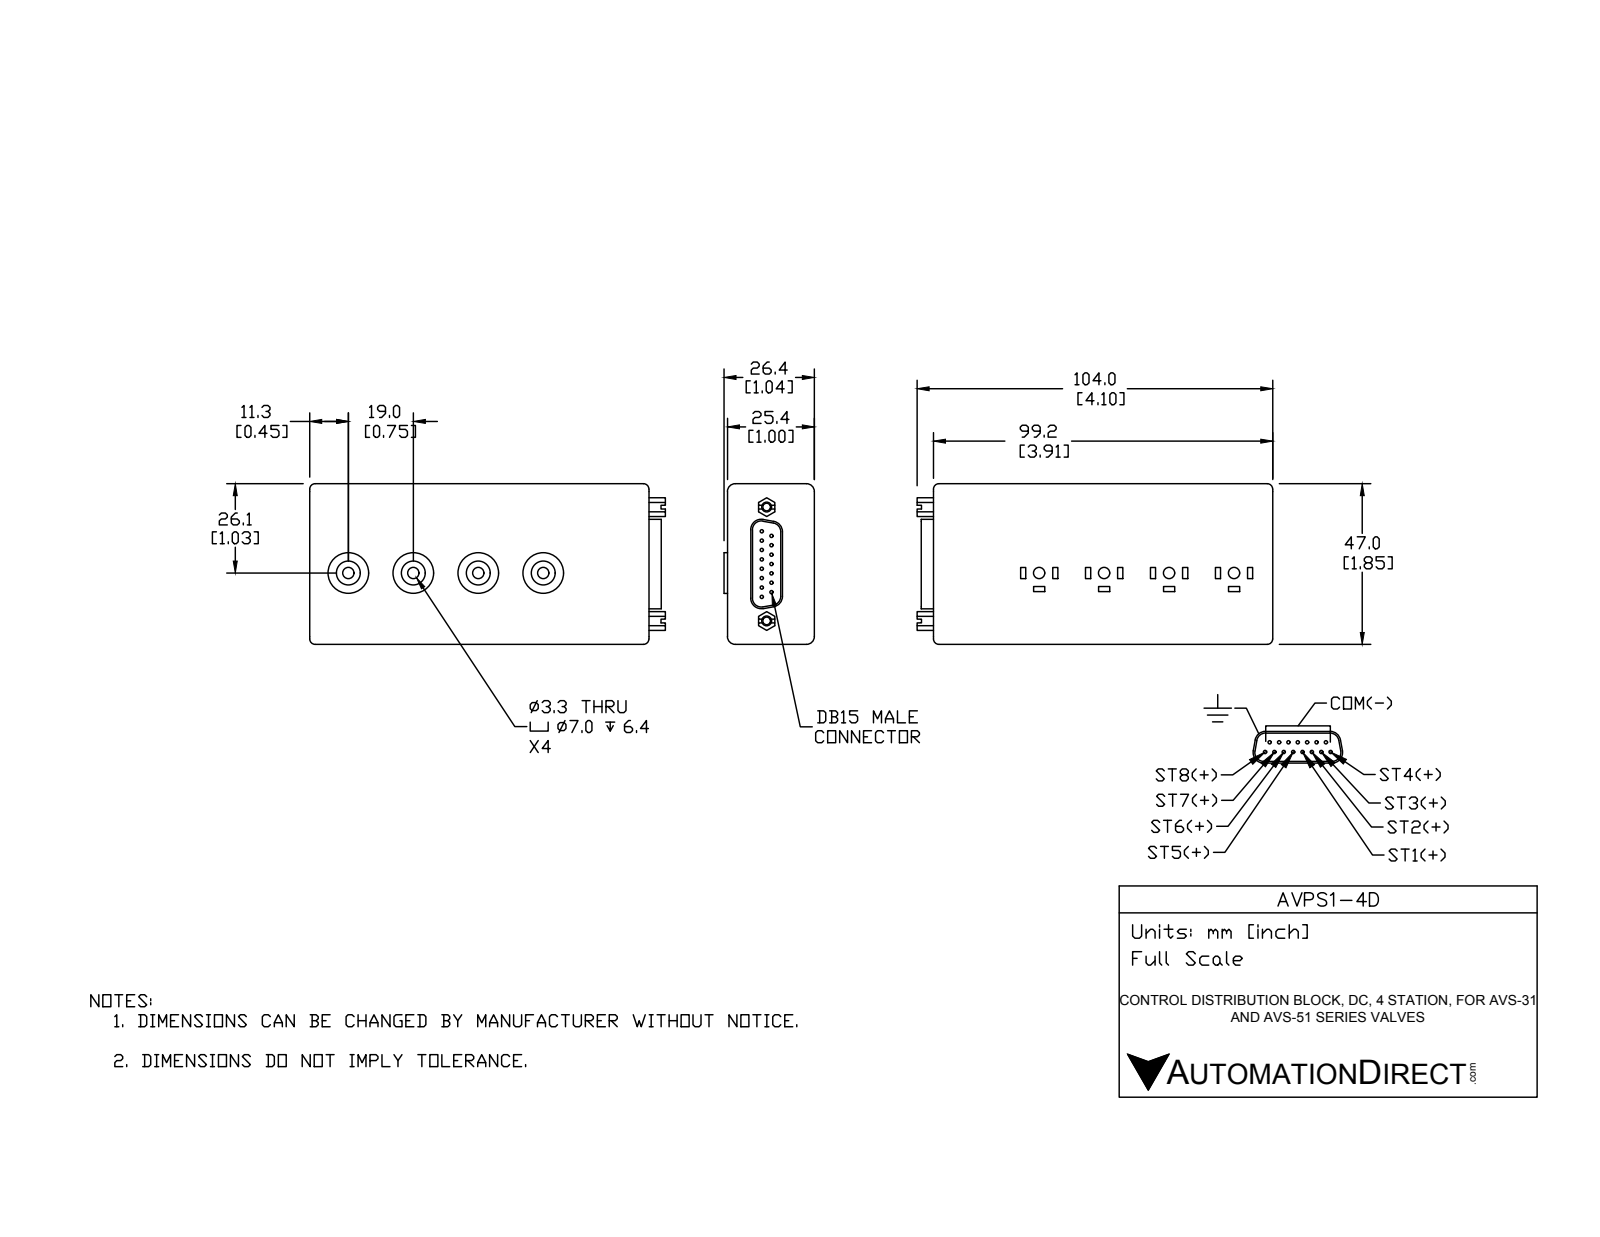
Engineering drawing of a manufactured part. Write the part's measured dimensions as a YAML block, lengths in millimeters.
part_name: "AVPS1-4D"
step_written_by: "SolidWorks 2016 (AUTOMOTIVE_DESIGN)"
units: millimeters
bodies: {solids: 1, faces: 219, planar: 127, cylindrical: 80, other: 12}
overall_size: [104, 47, 26.4]
volume: 116000
surface_area: 19490
round_holes:
  - {diameter: 3.3, count: 4}
  - {diameter: 7, count: 4}
  - {diameter: 2.3, count: 2}
round_bosses_or_shafts:
  - {diameter: 1, count: 15}
  - {diameter: 11.9, count: 4}
partial_cylinders:
  - {radius: 1.6, count: 6}
  - {radius: 2.3, count: 4}
  - {radius: 2.6, count: 4}
  - {radius: 3.1, count: 4}
  - {radius: 1.6, count: 2}
face_to_face_distances: [25.4, 47, 99.2, 1, 26.4, 1.5, 19, 3.1, 96.1, 6.4]
hole_center_spacings: [19, 38, 33.3, 57]
